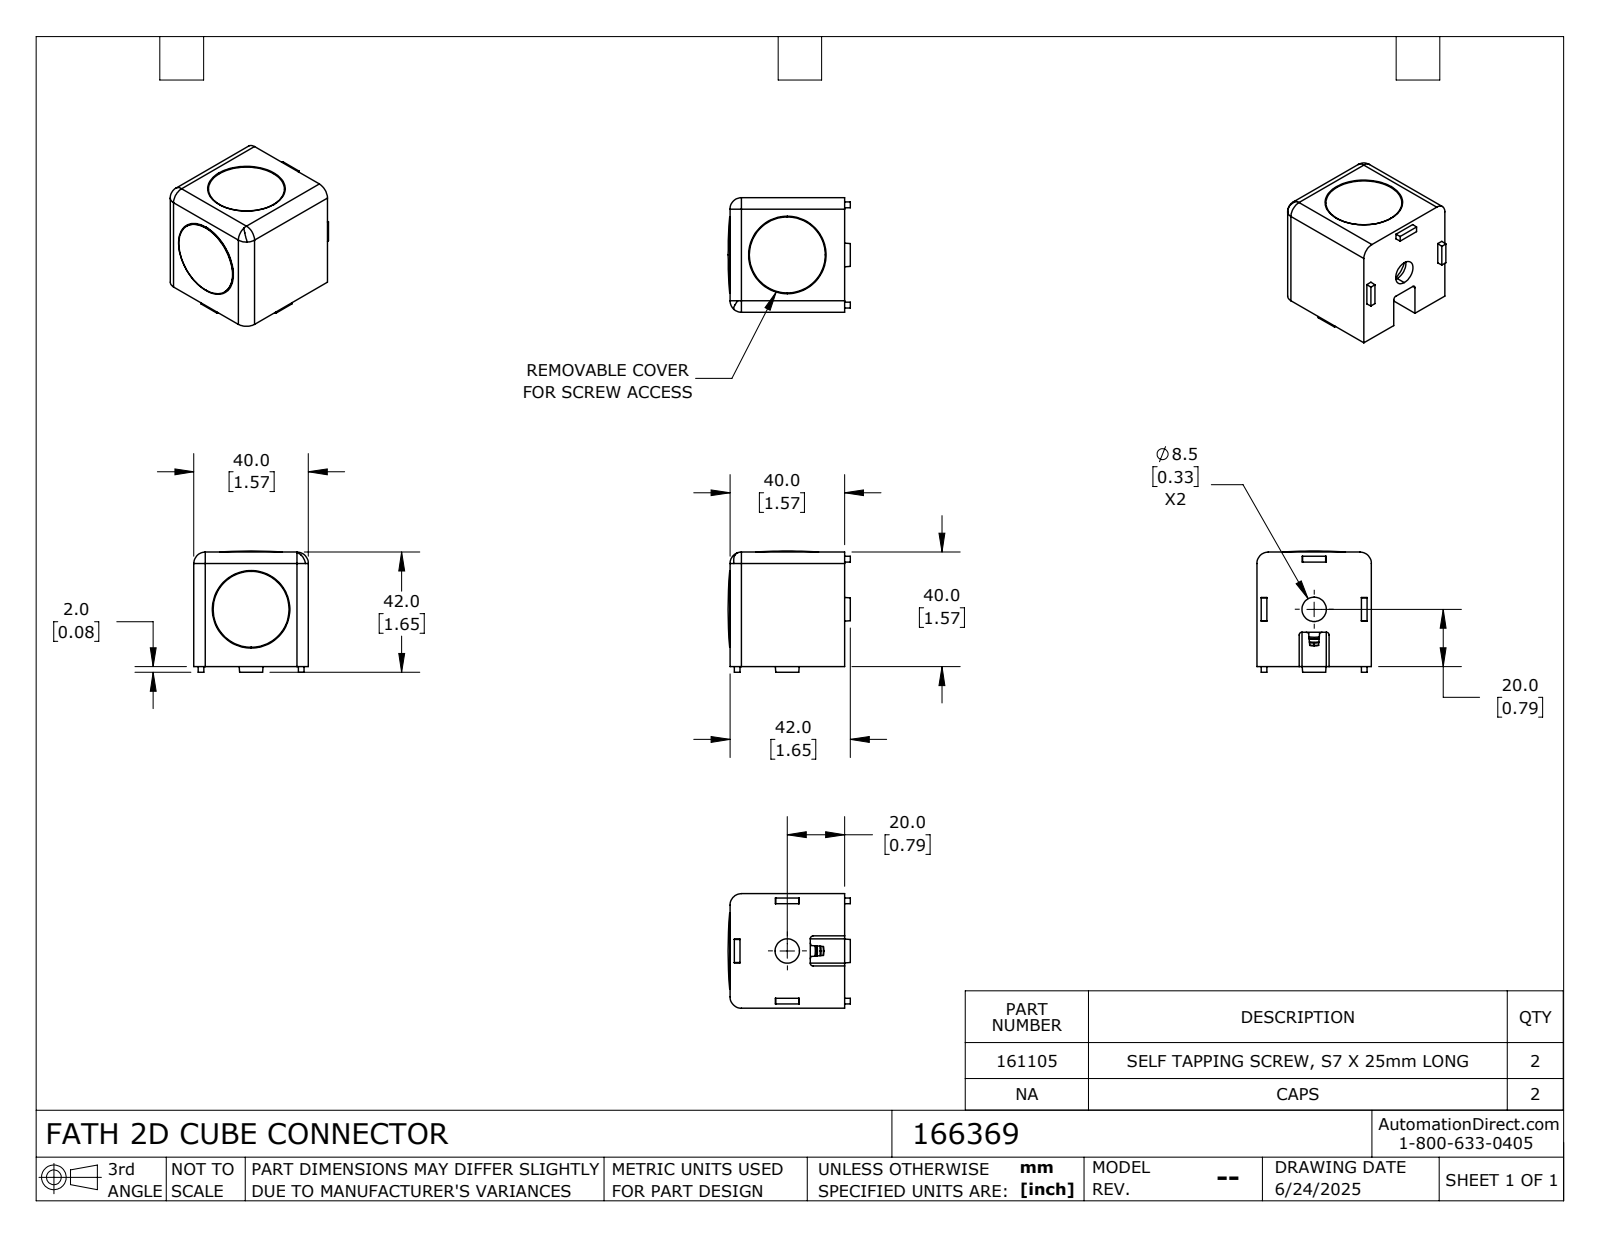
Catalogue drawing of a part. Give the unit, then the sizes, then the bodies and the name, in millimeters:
Units: millimetres
Overall size (bounding box): 42.65 × 42.34 × 40
Round holes (diameter × count): ⌀8.5 ×2
Round bosses / shafts (diameter × count): ⌀26.5 ×2, ⌀23 ×2
Partial cylindrical surfaces — rounded edges, fillets, slot ends (radius × count): R4 ×5, R1 ×4
Main face-to-face distances: 40, 39.15, 0.85, 38.84, 1.16, 14.75, 25.25, 2, 12, 28
Volume: 45 017 mm³ · Surface area: 15 892 mm²
Bodies: 3 solids, 155 faces (44 planar, 31 cylindrical, 80 other)
Part name (STEP PRODUCT): 166369
STEP written by: SolidWorks 2023 (CONFIG_CONTROL_DESIGN)
